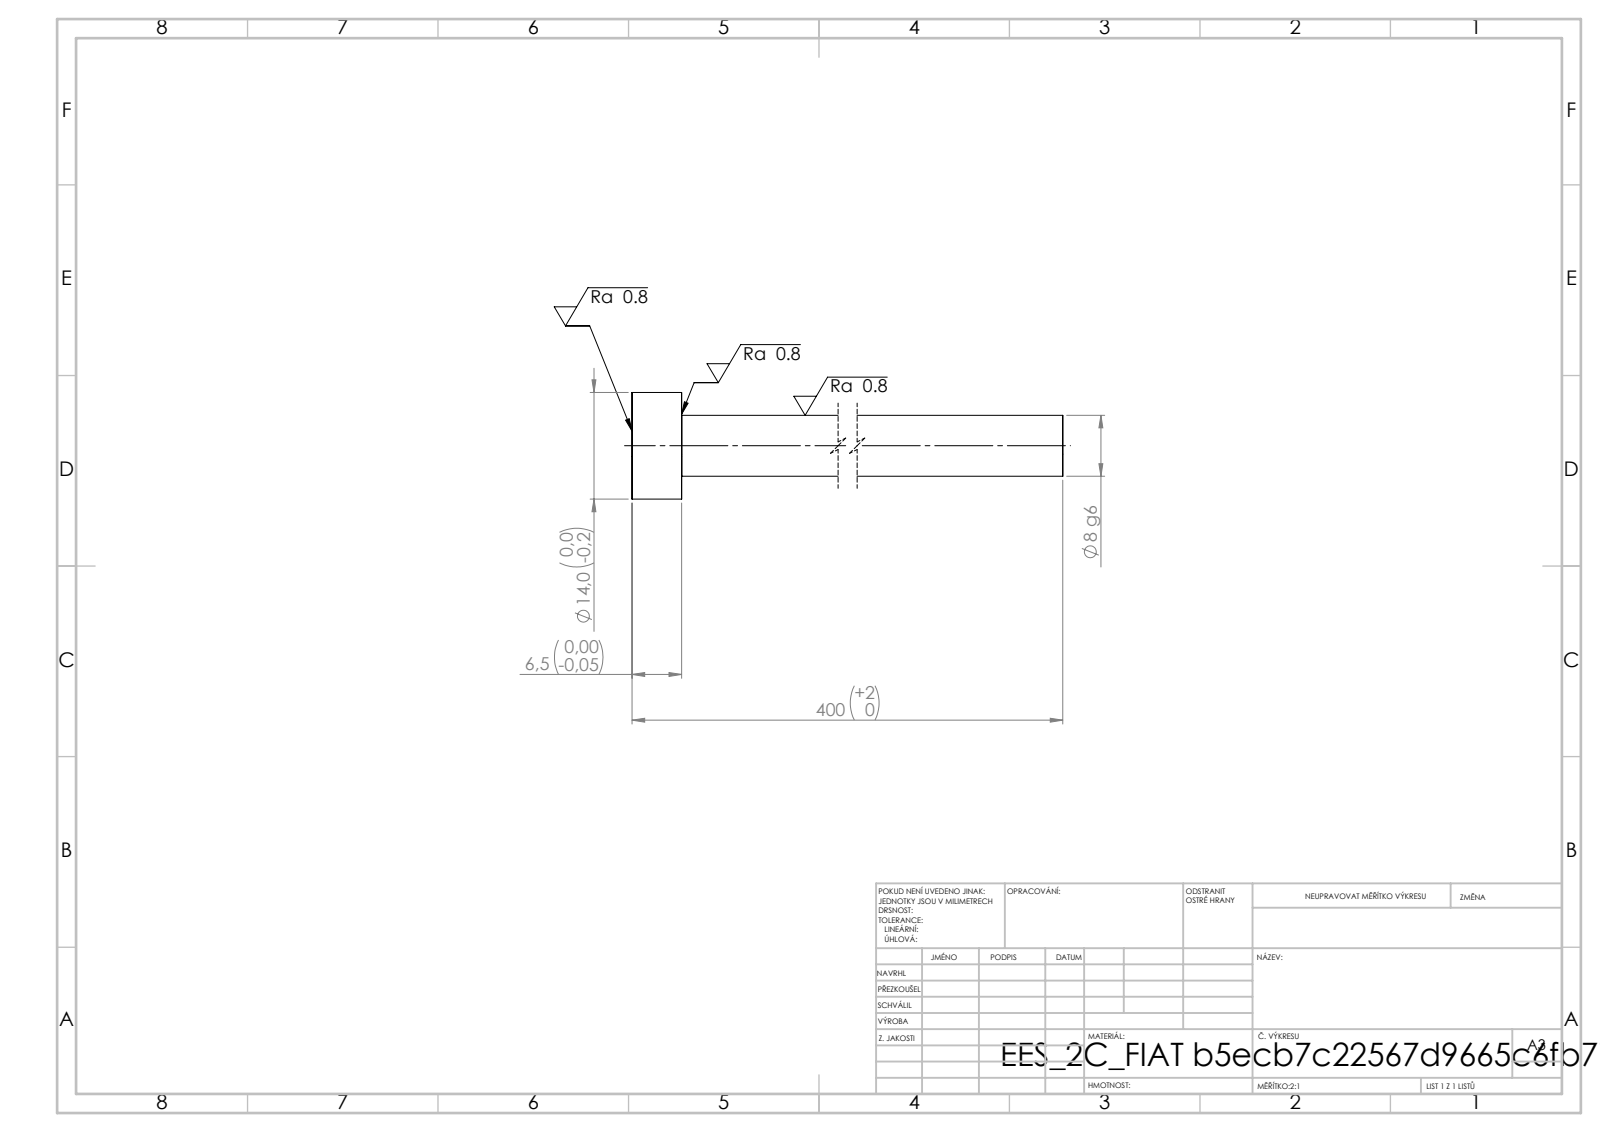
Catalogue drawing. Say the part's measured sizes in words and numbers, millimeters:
Its 3-D file was written by "SolidWorks 2019 (CONFIG_CONTROL_DESIGN)". It is 1 solid with 7 faces: 3 planar, 4 cylindrical and 0 other. Overall it measures 400 by 14 by 14 millimeters. Its volume is 20 780 cubic millimeters and its surface area 10 483 square millimeters. Round bosses or shafts: 1 of diameter 14, 1 of diameter 8. The main face-to-face distances are 6.5, 400, 393.5.
